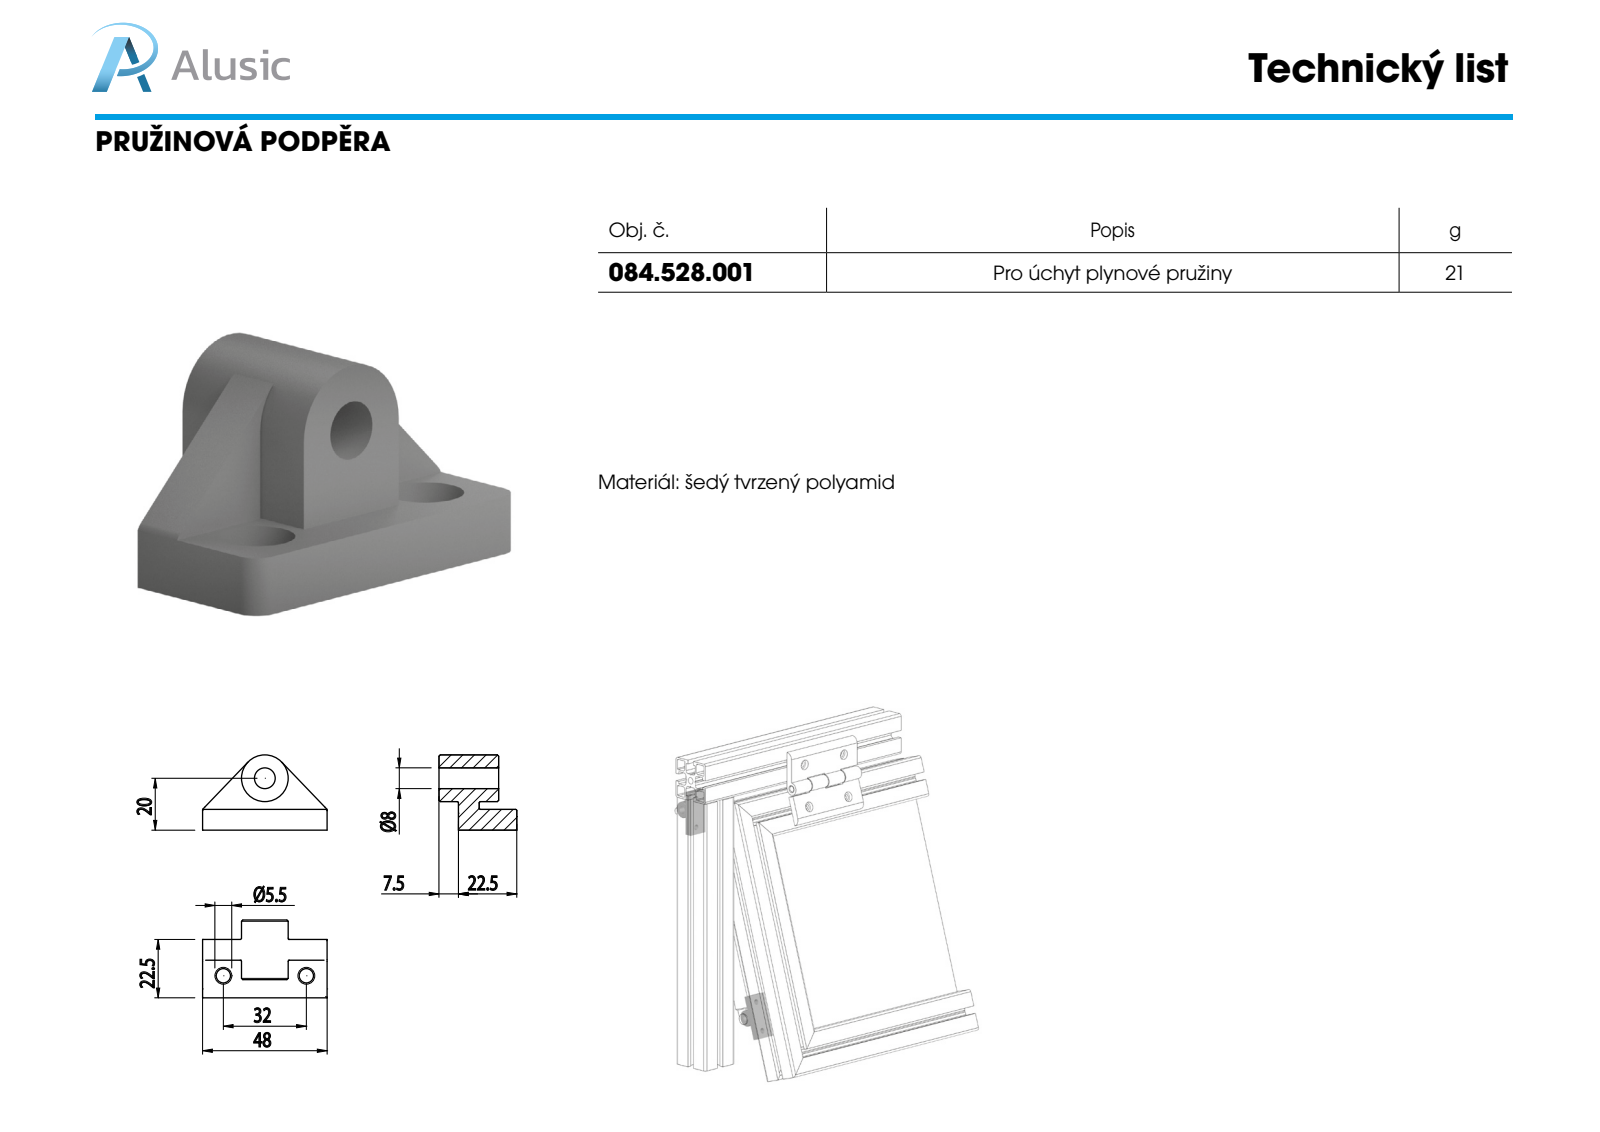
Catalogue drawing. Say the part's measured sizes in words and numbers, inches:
The part is named "084.528.001". Its 3-D file was written by "SolidWorks 2011 (CONFIG_CONTROL_DESIGN)". It is 1 solid with 56 faces: 11 planar, 18 cylindrical and 27 other. Overall it measures 1.89 by 1.181 by 1.142 inches. Its volume is 0.948 cubic inches and its surface area 9.274 square inches. Round holes: 2 of diameter 0.217, 1 of diameter 0.315. Round bosses or shafts: 1 of diameter 0.709. Partial cylindrical surfaces (rounded edges, fillets, slot ends): 9 of radius 0.02. The main face-to-face distances are 0.315, 0.886, 0.295, 0.61, 0.571, 0.906, 1.181, 0.276, 1.89. The hole center spacings are 1.26.
